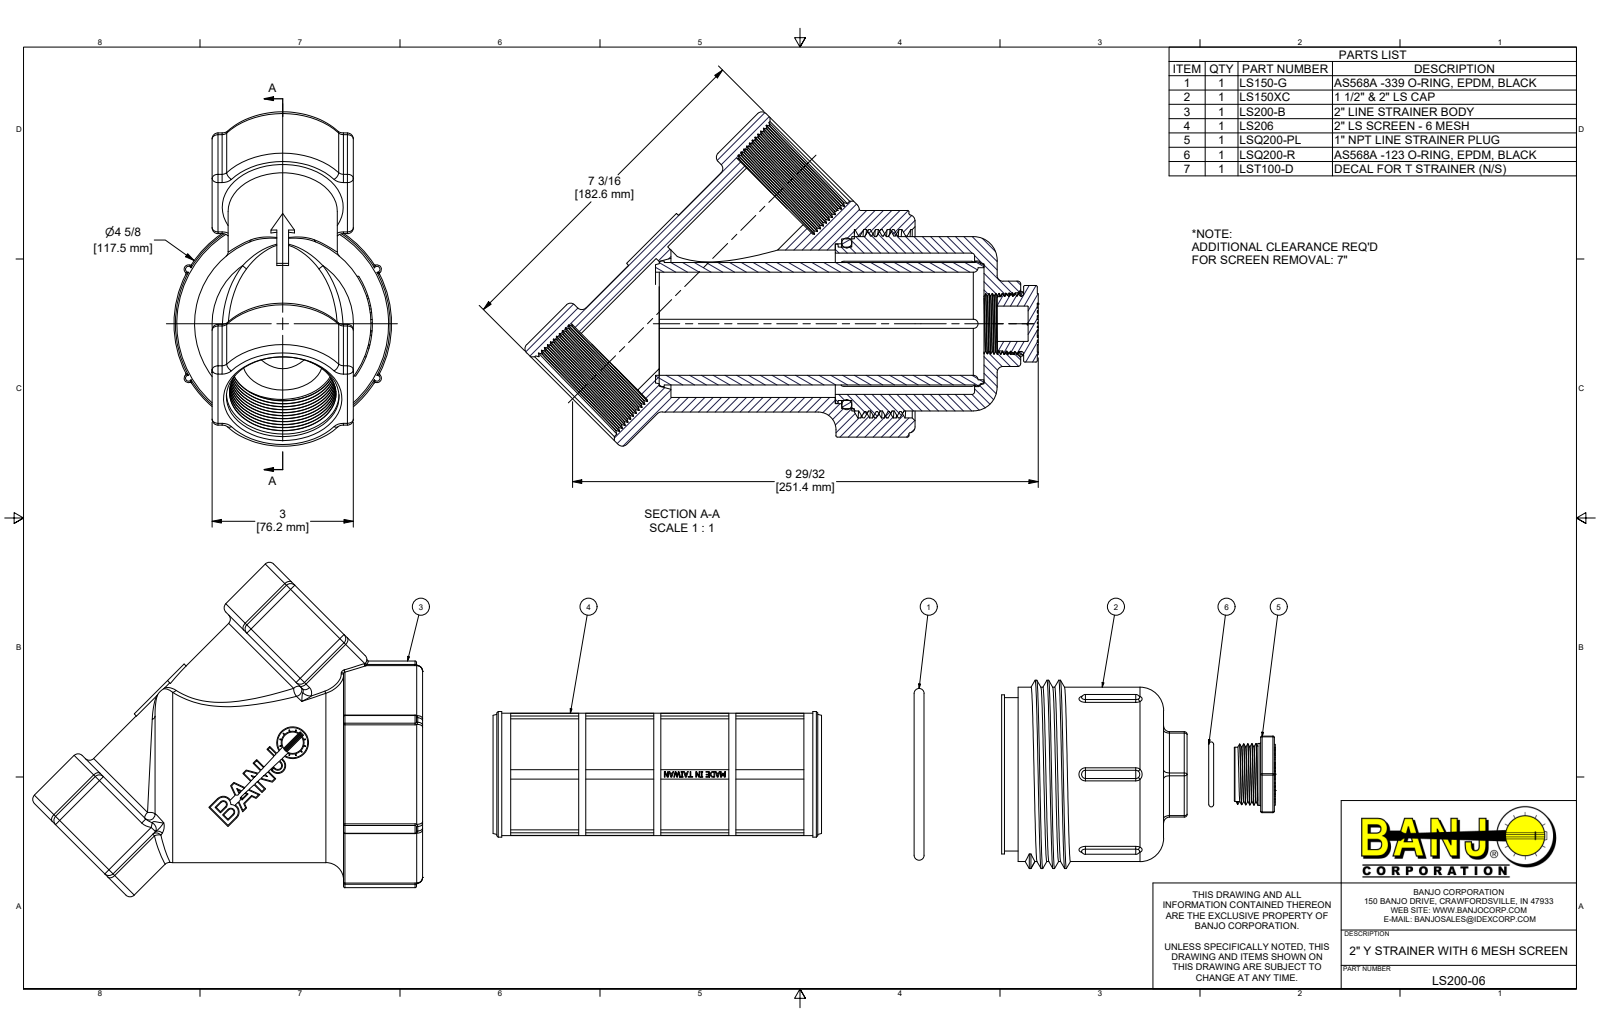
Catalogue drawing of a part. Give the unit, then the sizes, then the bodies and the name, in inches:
Units: inches
Overall size (bounding box): 21.59 × 7.102 × 4.625
Round holes (diameter × count): ⌀1.7 ×2, ⌀0.454 ×1, ⌀0.641 ×1, ⌀0.75 ×1, ⌀2.19 ×1, ⌀2.35 ×1, ⌀3 ×1, ⌀3.13 ×1, ⌀3.395 ×1, ⌀3.605 ×1, ⌀3.729 ×1, ⌀4 ×1
Round bosses / shafts (diameter × count): ⌀4.625 ×1, ⌀3.75 ×1, ⌀3.702 ×1, ⌀3.38 ×1, ⌀3.257 ×1, ⌀2.666 ×1, ⌀2.6 ×1, ⌀2.38 ×1
Partial cylindrical surfaces — rounded edges, fillets, slot ends (radius × count): R0.06 ×46, R0.125 ×35, R0.03 ×30, R0.094 ×12, R0.1 ×4, R0.12 ×3, R0.065 ×2, R0.082 ×2
Main face-to-face distances: 3, 3.16, 1.745, 1.595, 2.785, 1.445, 1.34, 0.2, 0.35, 2.81
Volume: 56.03 in³ · Surface area: 657.3 in²
Bodies: 6 solids, 1732 faces (838 planar, 279 cylindrical, 615 other)
Part name (STEP PRODUCT): LS200-06; LS200-B; LS150-C; LS150XC (+4 more)
STEP written by: Autodesk Inventor 2019 (AUTOMOTIVE_DESIGN)
